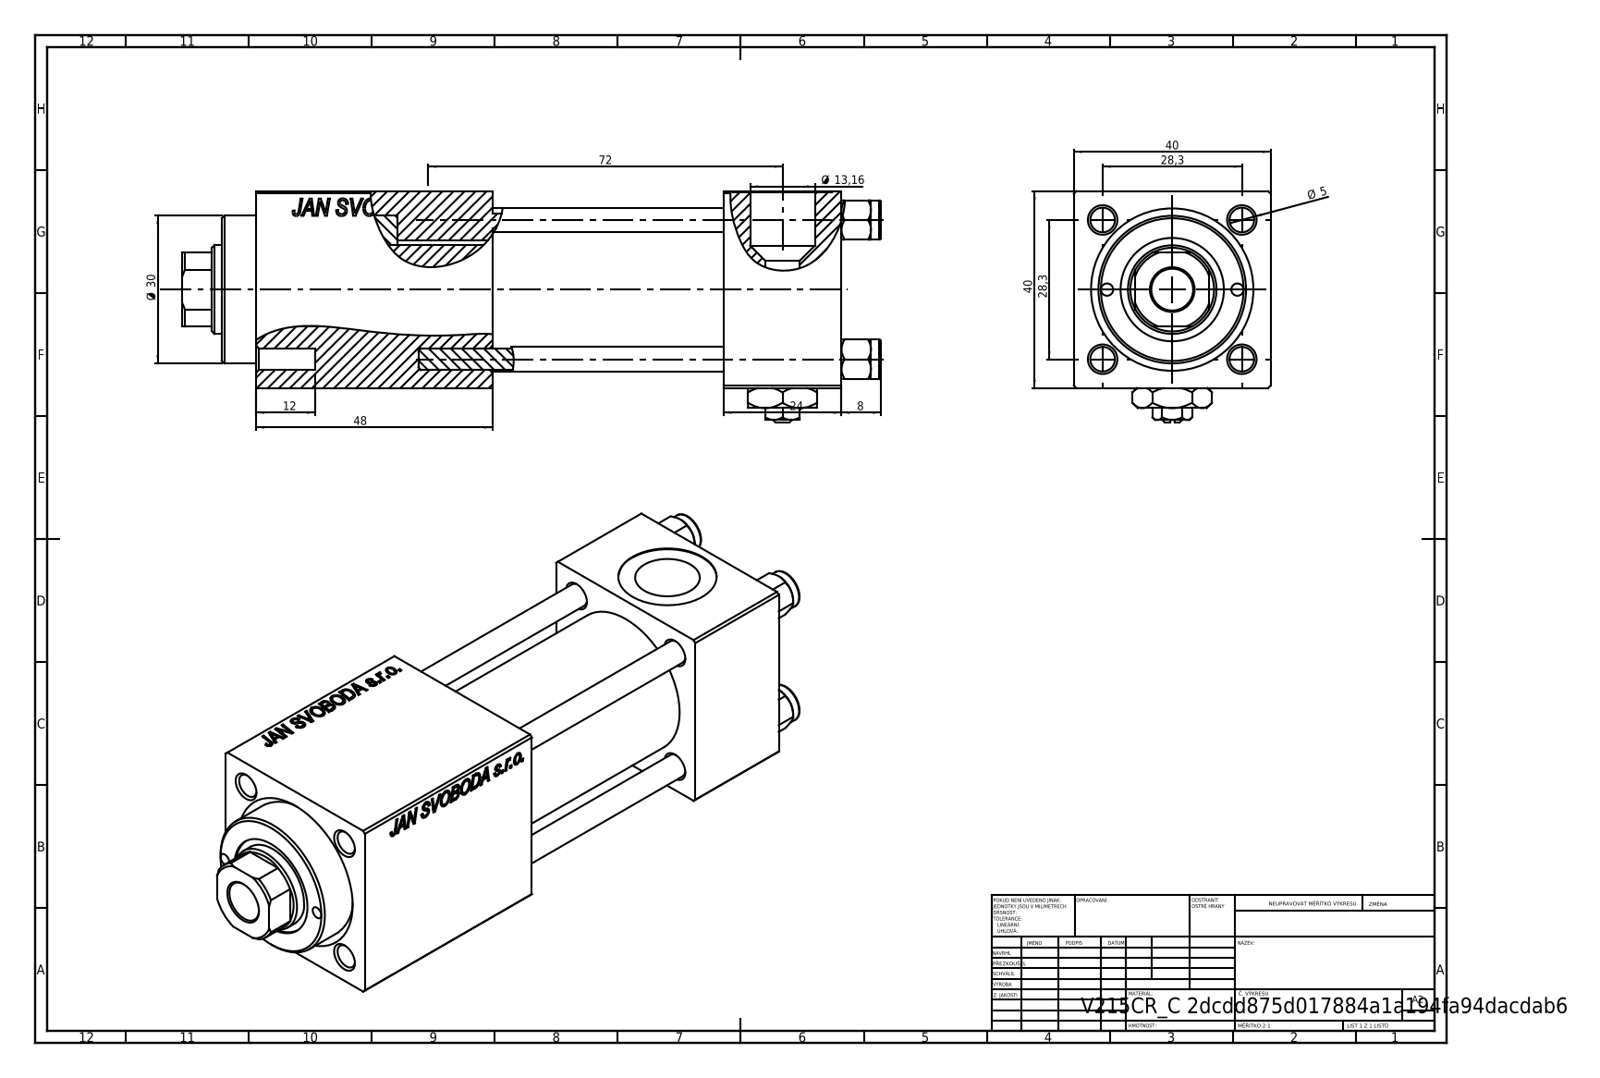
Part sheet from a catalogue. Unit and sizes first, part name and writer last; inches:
Units: inches
Overall size (bounding box): 5.591 × 1.85 × 1.575
Round holes (diameter × count): ⌀0.197 ×4, ⌀0.787 ×3, ⌀0.098 ×2, ⌀0.276 ×2, ⌀0.518 ×2, ⌀0.335 ×1, ⌀0.709 ×1, ⌀0.827 ×1, ⌀0.984 ×1, ⌀1.181 ×1
Round bosses / shafts (diameter × count): ⌀0.315 ×4, ⌀1.22 ×1
Partial cylindrical surfaces — rounded edges, fillets, slot ends (radius × count): R0.335 ×1
Main face-to-face distances: 1.575, 0.945, 2.795, 1.85, 3.555, 2.61, 0.76, 1.89, 1.567, 3.74
Hole centre spacings: 0.558, 0.788, 1.114, 1.214, 0.522, 1.576, 1.043, 2.835
Volume: 9.076 in³ · Surface area: 89.89 in²
Bodies: 12 solids, 1203 faces (549 planar, 96 cylindrical, 558 other)
Part name (STEP PRODUCT): V215CR_C_Body; V215CR_C_TYCINKA; NUT_M5_C; V215CR_VCP_C (+2 more)
STEP written by: SolidWorks 2019 (CONFIG_CONTROL_DESIGN)
